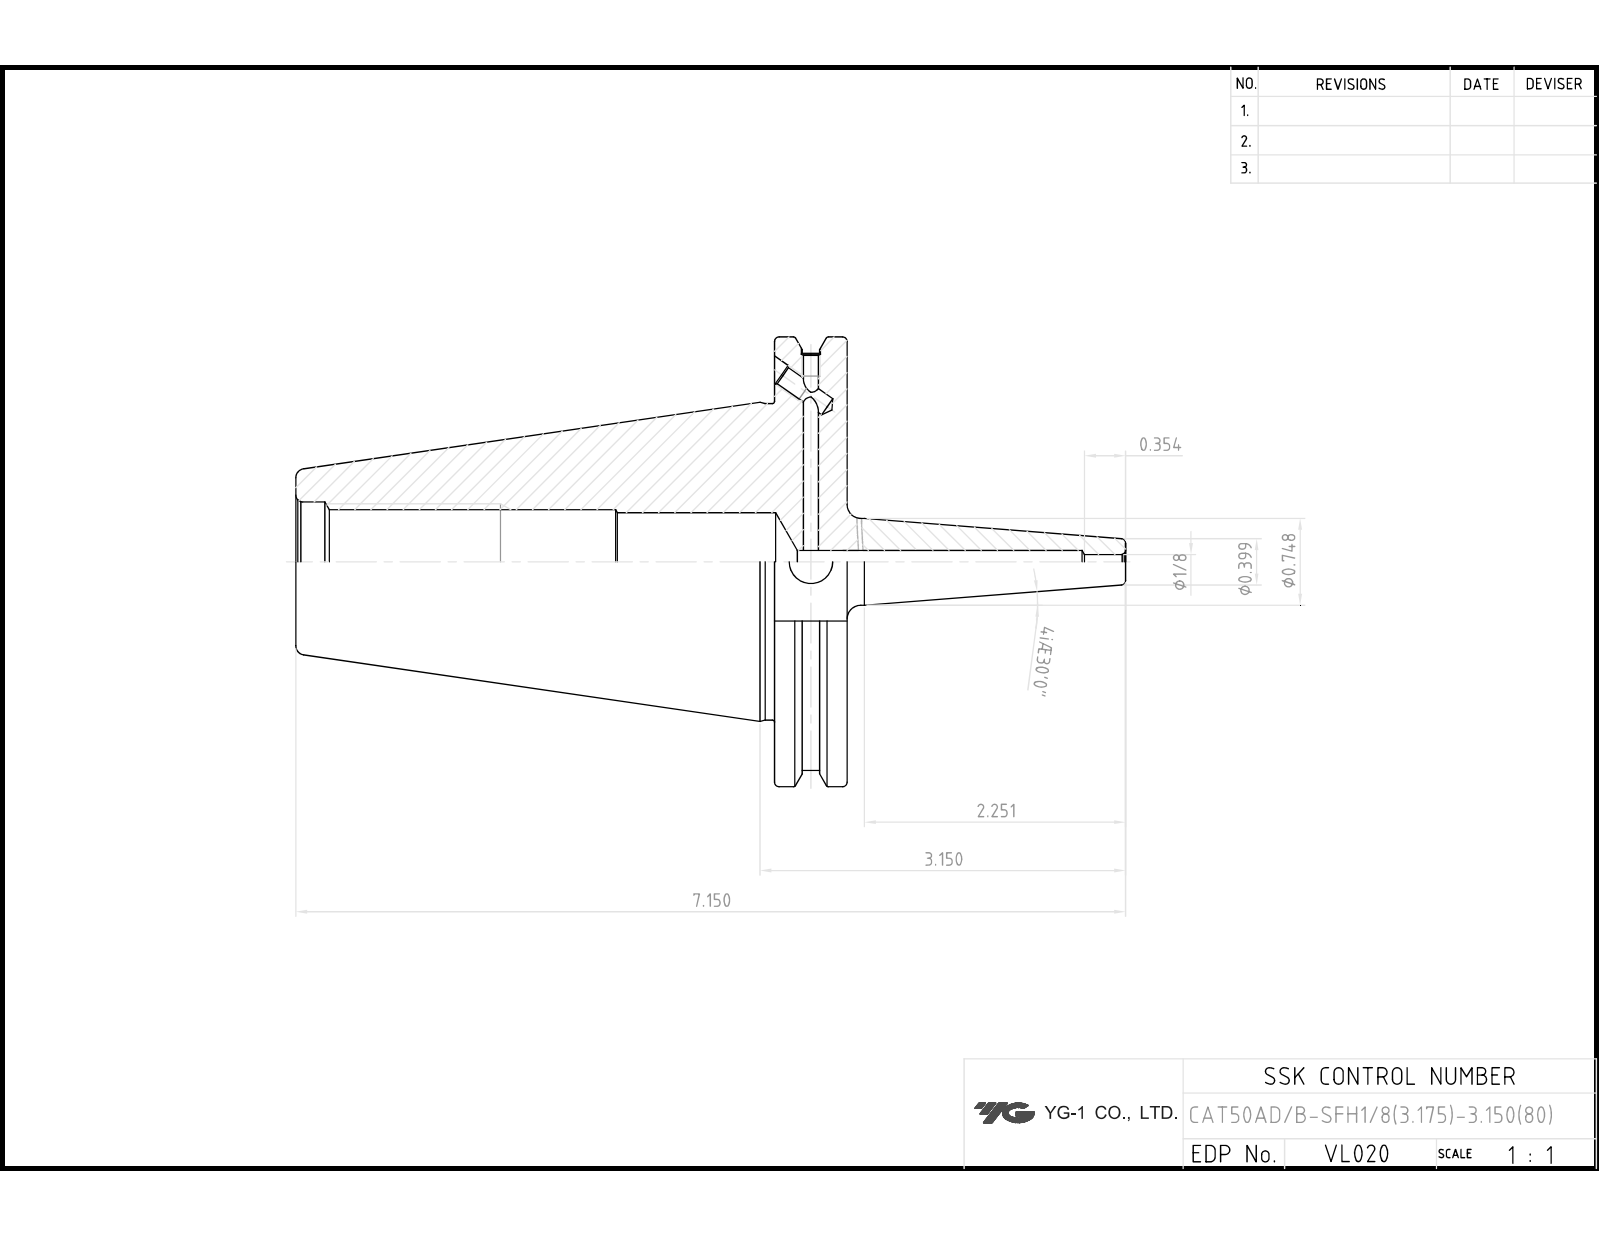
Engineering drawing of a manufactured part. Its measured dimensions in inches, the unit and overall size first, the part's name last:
Units: inches
Overall size (bounding box): 7.15 × 3.875 × 3.728
Round holes (diameter × count): ⌀0.197 ×3, ⌀0.128 ×2, ⌀0.163 ×2, ⌀0.165 ×2, ⌀0.125 ×1, ⌀0.375 ×1, ⌀0.846 ×1, ⌀0.865 ×1, ⌀1.031 ×1
Round bosses / shafts (diameter × count): ⌀3.875 ×1, ⌀3.594 ×1, ⌀2.726 ×1, ⌀0.748 ×1
Main face-to-face distances: 0.625, 4.125, 4.75, 2.875, 1.02, 4.363, 0.238, 0.387, 4.514, 0.389
Volume: 20.27 in³ · Surface area: 75.24 in²
Bodies: 1 solid, 84 faces (35 planar, 26 cylindrical, 23 other)
Part name (STEP PRODUCT): LO-CAT50ADB-SFH3.175-80
STEP written by: Autodesk Inventor 2024 (AUTOMOTIVE_DESIGN)
